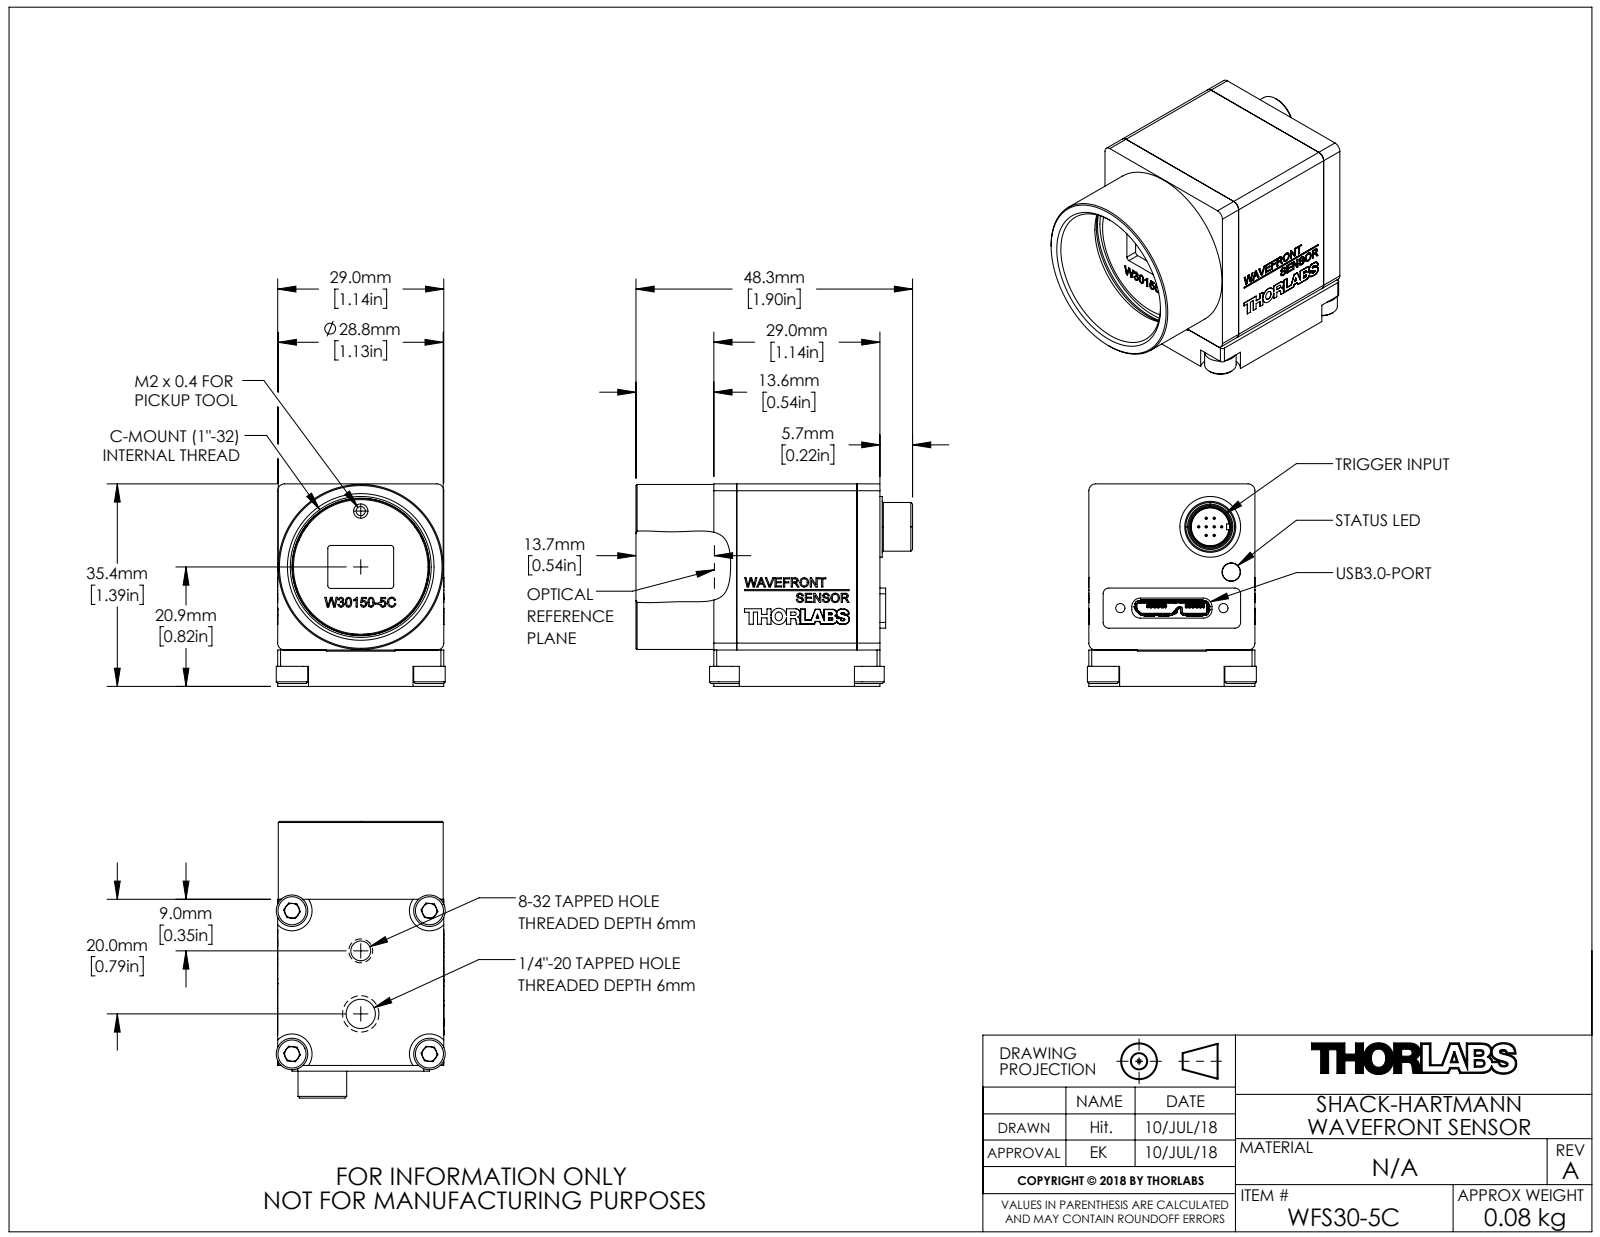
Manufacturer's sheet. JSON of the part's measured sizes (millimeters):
{"part_name": "MTN008509 WFS30-5C", "step_written_by": "SolidWorks 2016 (AUTOMOTIVE_DESIGN)", "units": "millimeters", "bodies": {"solids": 0, "faces": 2591, "planar": 1880, "cylindrical": 402, "other": 309}, "overall_size": [48.3, 35.35, 29.5], "round_holes": [[3.2, 11], [2.5, 5], [1.6, 3], [1.9, 3], [0.95, 1], [1.5, 1], [3.45, 1], [5.11, 1], [6.8, 1], [8, 1], [15, 1], [24, 1]], "round_bosses_or_shafts": [[0.4, 8], [1, 6], [3, 5], [5.5, 4], [28.8, 1], [23.9, 1], [23.5, 1], [15.4, 1]], "partial_cylinders_radius": [[0.5, 37], [0.2, 31], [0.15, 29], [0.3, 12], [1, 11], [1.5, 10], [0.1, 8], [0.6, 8]], "face_to_face_distances": [29, 0.6, 28.4, 6.35, 4.8, 35.35, 2.62, 27.8, 17.57, 22.37], "hole_center_spacings": [9.75, 18.83, 9.74, 13.79, 16.88, 5.04, 13.89, 21.63]}
